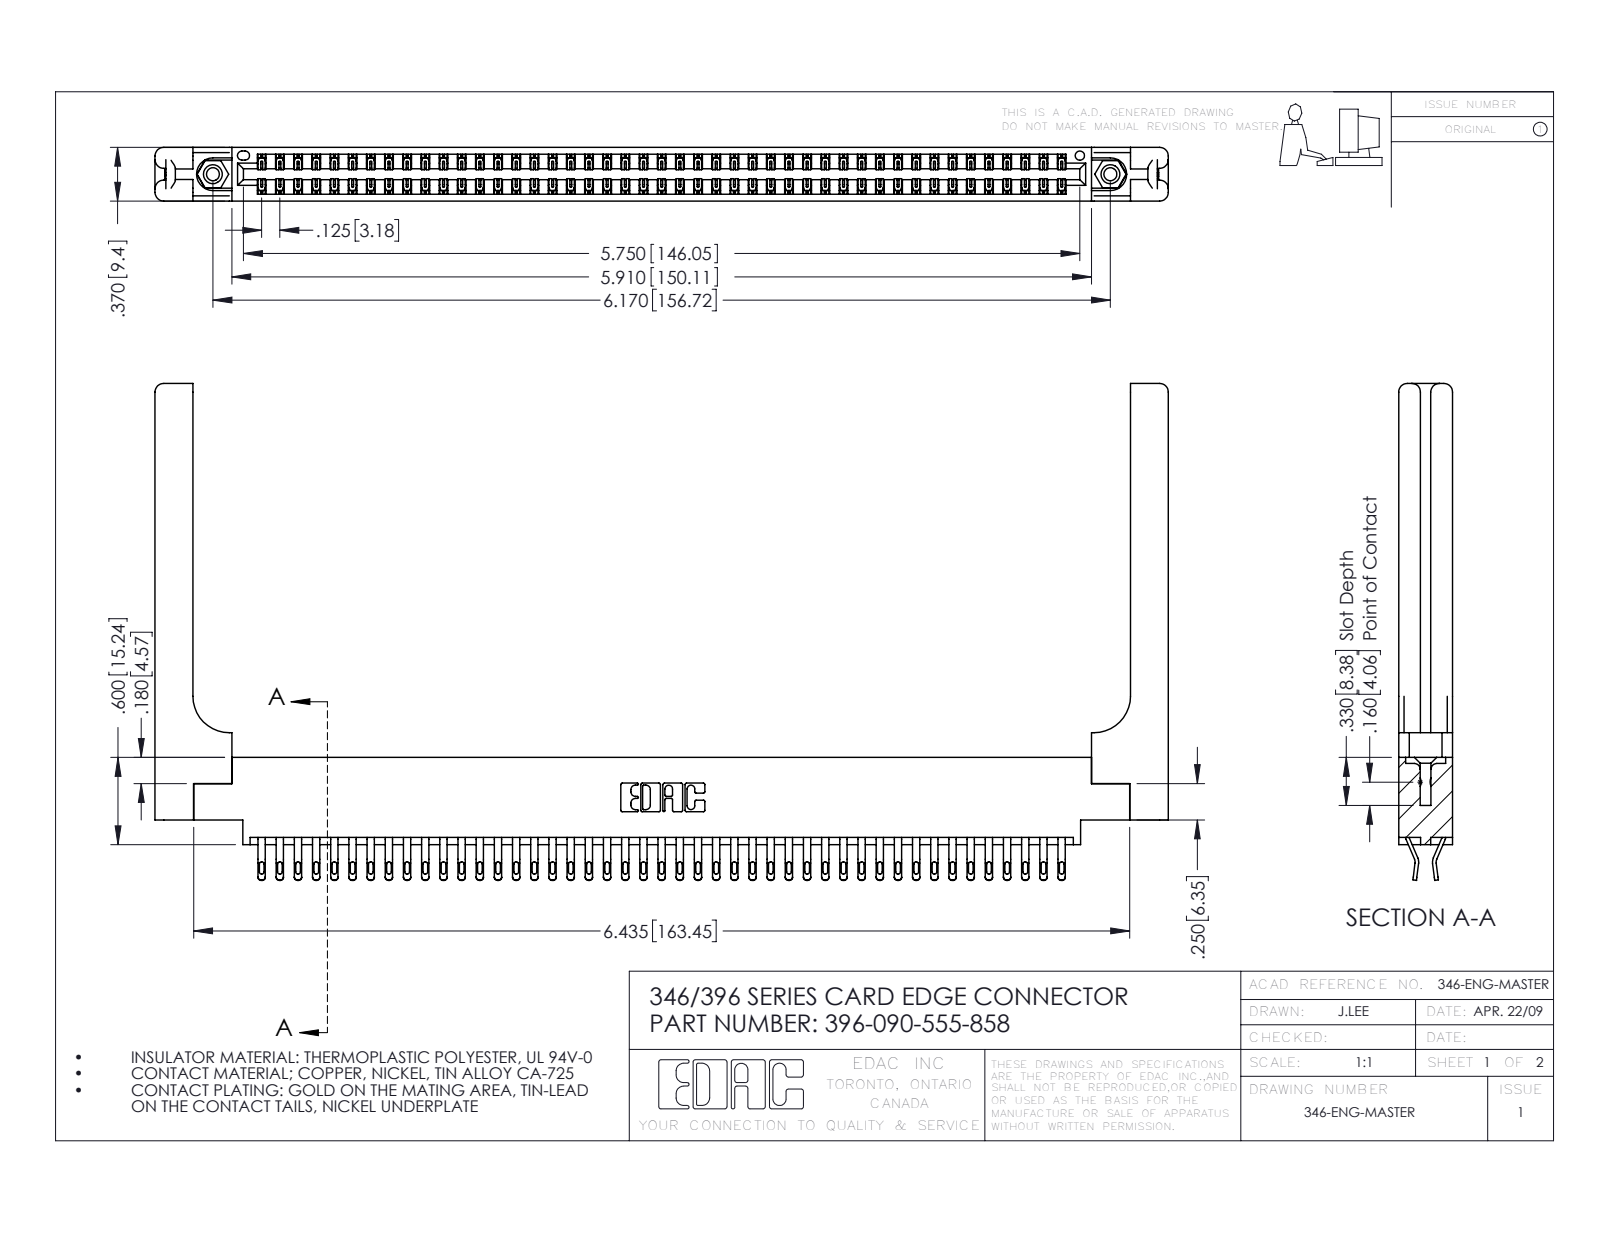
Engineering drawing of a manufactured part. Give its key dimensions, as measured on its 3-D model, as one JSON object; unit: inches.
{"part_name": "345-292-001_555 Tail; 346-220-058_345-220-058; 346 Part_0.170 Offset - 0.156 Dia-TH; 345-250-001_345-250-001-102 (+1 more)", "step_written_by": "SolidWorks 2016 (CONFIG_CONTROL_DESIGN)", "units": "inches", "bodies": {"solids": 95, "faces": 5602, "planar": 3198, "cylindrical": 2344, "other": 60}, "overall_size": [6.966, 3.415, 0.37], "volume_in3": 1.518, "surface_area_in2": 46.54, "round_holes": [[0.089, 2], [0.125, 2], [0.156, 2], [0.064, 1]], "round_bosses_or_shafts": [[0.155, 2]], "partial_cylinders_radius": [[0.016, 180], [0.02, 180], [0.006, 135], [0.01, 22], [0.06, 16], [0.007, 6], [0.031, 6], [0.026, 3]], "face_to_face_distances": [0.37, 0.048, 0.322, 0.072, 0.148, 0.15, 0.25, 0.025, 0.298, 0.275], "hole_center_spacings": [0.246, 5.961, 6.17]}
